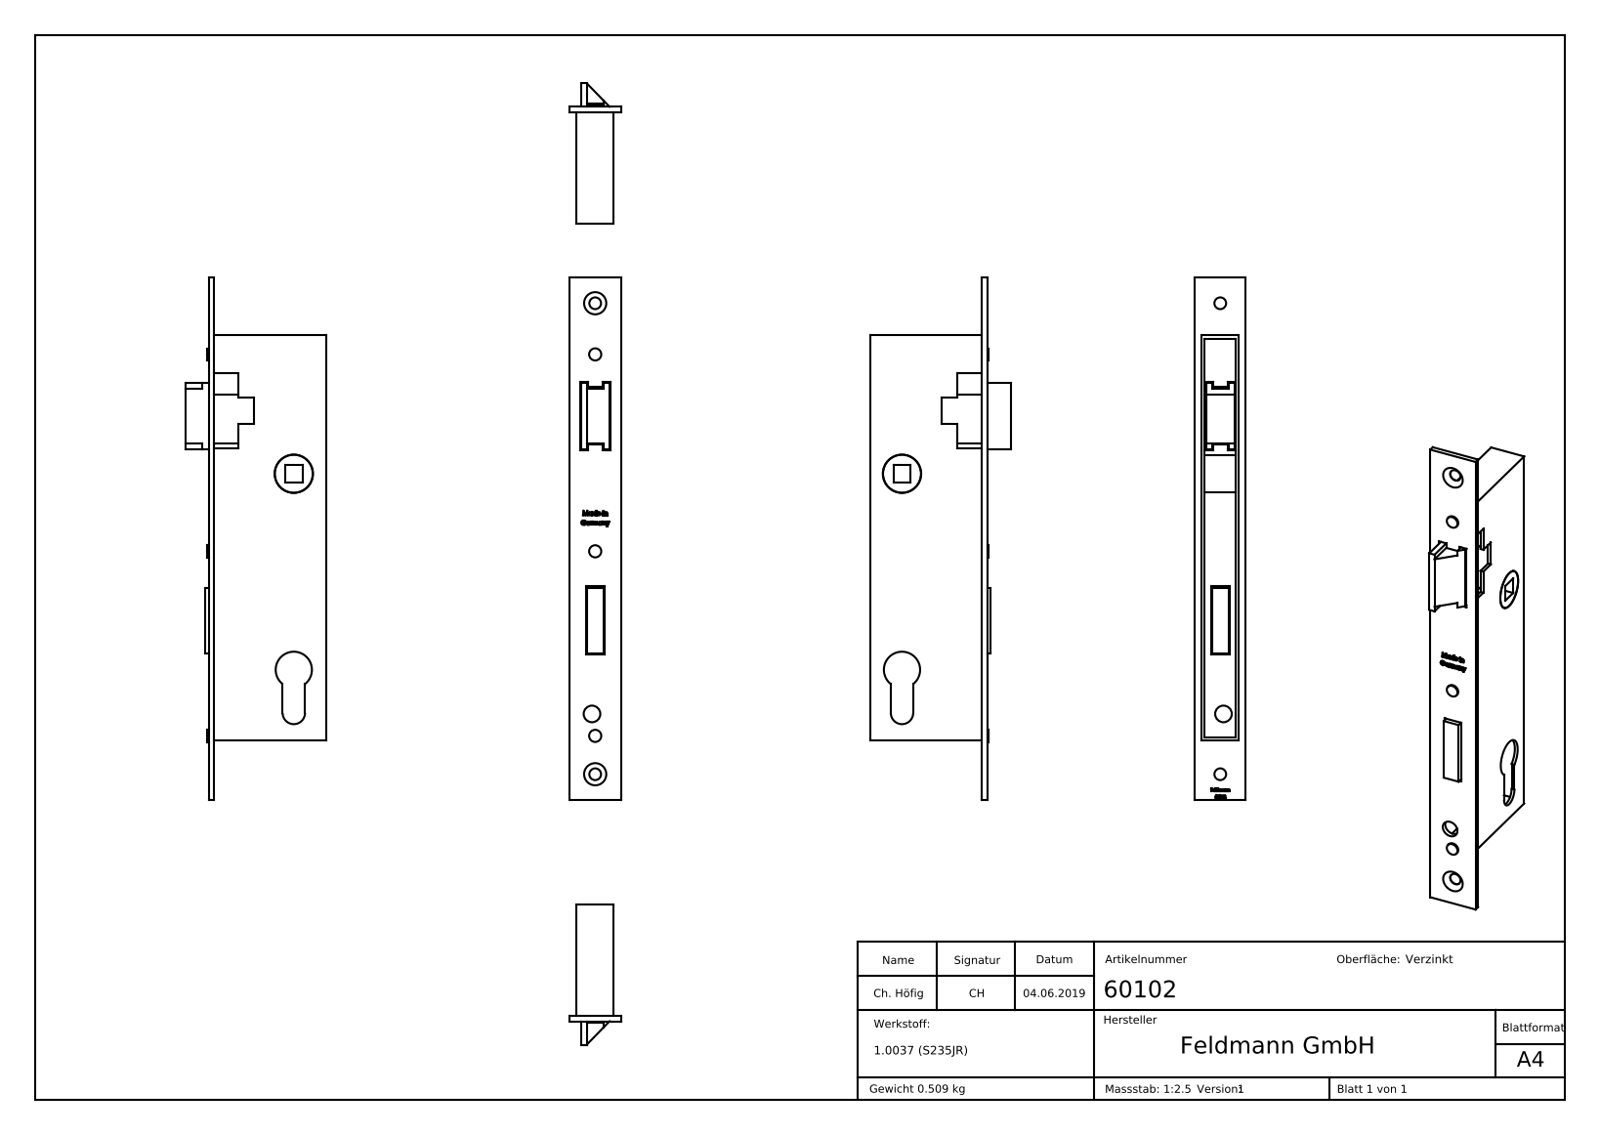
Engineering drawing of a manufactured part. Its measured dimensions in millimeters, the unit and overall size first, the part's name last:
Units: millimetres
Overall size (bounding box): 245 × 66 × 24
Round holes (diameter × count): ⌀5.5 ×2, ⌀7.8 ×1, ⌀18 ×1
Round bosses / shafts (diameter × count): ⌀5.7 ×3, ⌀17.8 ×1
Partial cylindrical surfaces — rounded edges, fillets, slot ends (radius × count): R5.25 ×1, R8.5 ×1
Main face-to-face distances: 1.5, 16, 17.5, 14.5, 2.5, 11.15, 0.5, 4.85, 12.65, 3.35
Hole centre spacings: 28.34, 192.71, 221
Volume: 65 240 mm³ · Surface area: 60 157 mm²
Bodies: 4 solids, 466 faces (272 planar, 24 cylindrical, 170 other)
Part name (STEP PRODUCT): 60102
STEP written by: SolidWorks 2015 (CONFIG_CONTROL_DESIGN)
